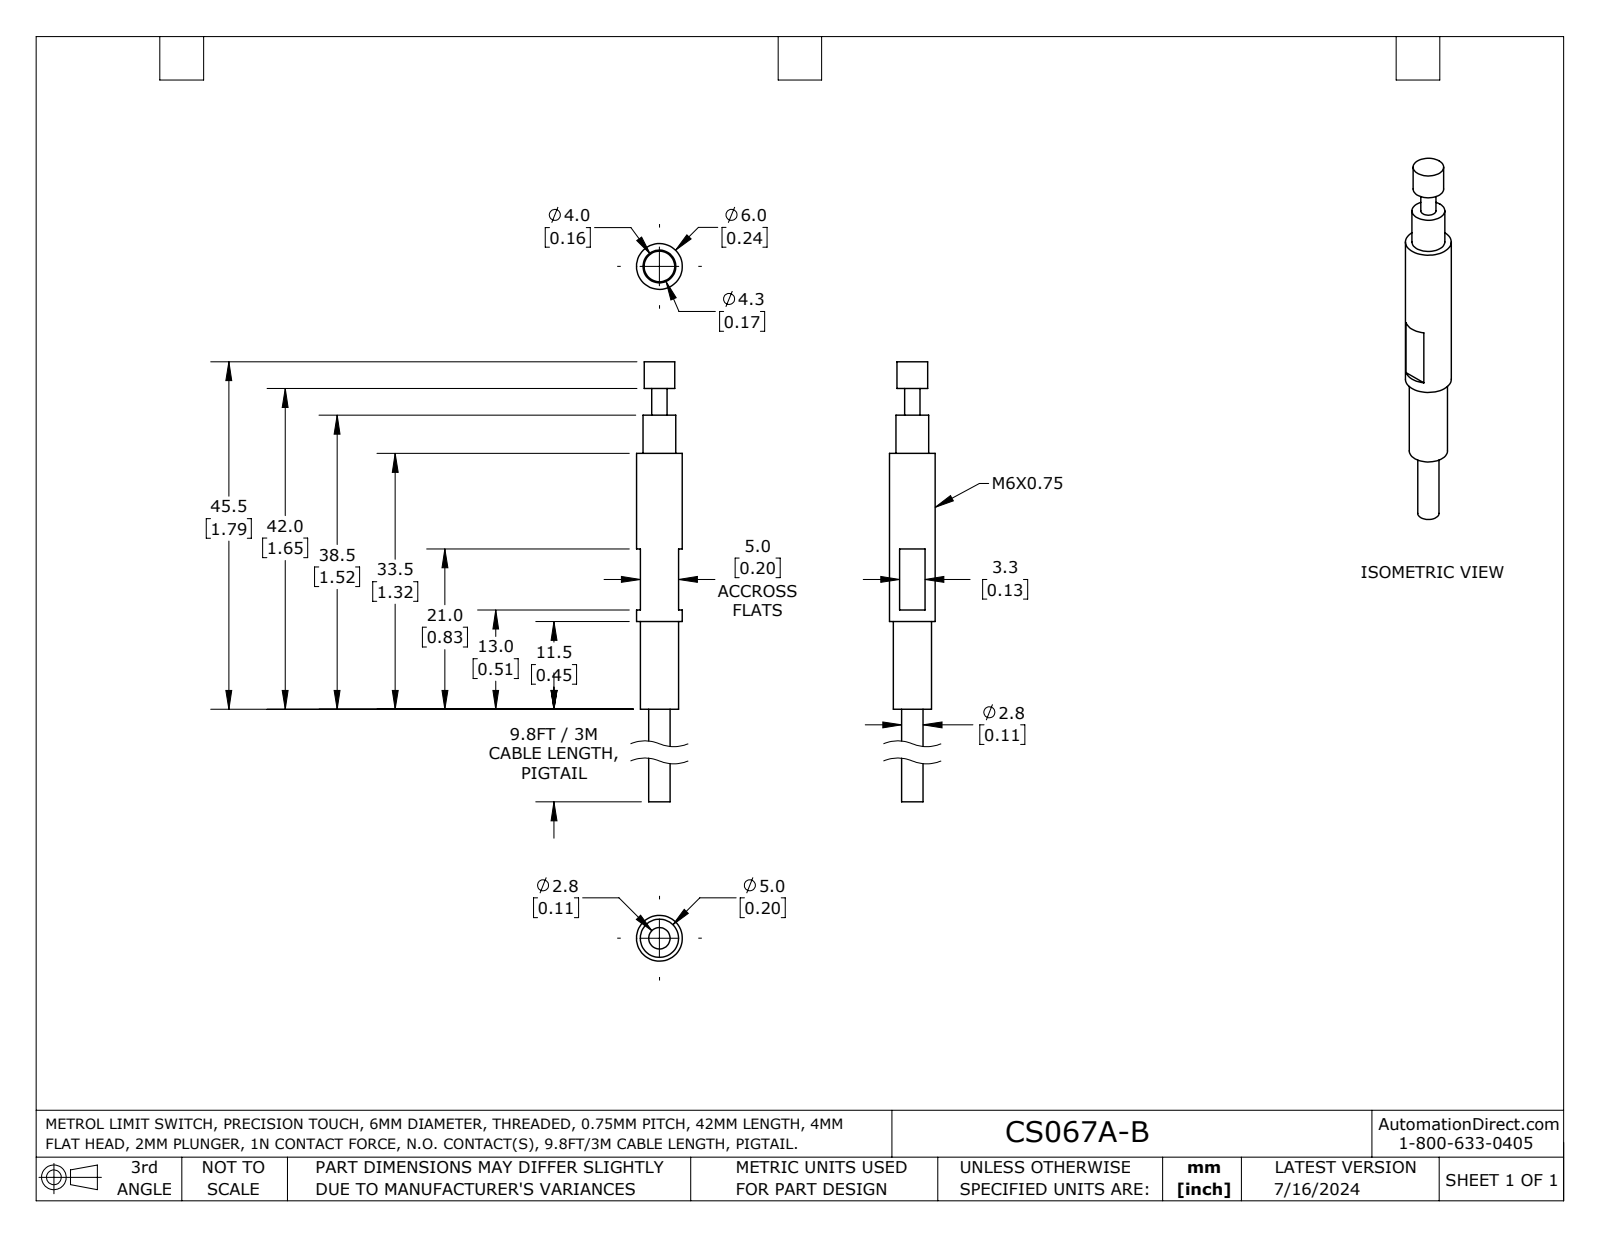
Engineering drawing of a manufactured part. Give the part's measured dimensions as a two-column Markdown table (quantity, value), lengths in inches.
| quantity | value |
| --- | --- |
| part name | CS067A-B |
| STEP written by | SolidWorks 2023 (AUTOMOTIVE_DESIGN) |
| units | inches |
| bodies | 1 solid, 19 faces (13 planar, 6 cylindrical, 0 other) |
| overall size | 2.185 × 0.236 × 0.236 |
| volume | 0.062 in³ |
| surface area | 1.39 in² |
| round bosses / shafts (diameter × count) | 0.236 × 1, 0.197 × 1, 0.169 × 1, 0.157 × 1, 0.11 × 1, 0.079 × 1 |
| main face-to-face distances | 0.197, 0.138, 1.319, 1.791, 0.472, 1.516, 0.276, 1.654, 0.335, 0.453 |
